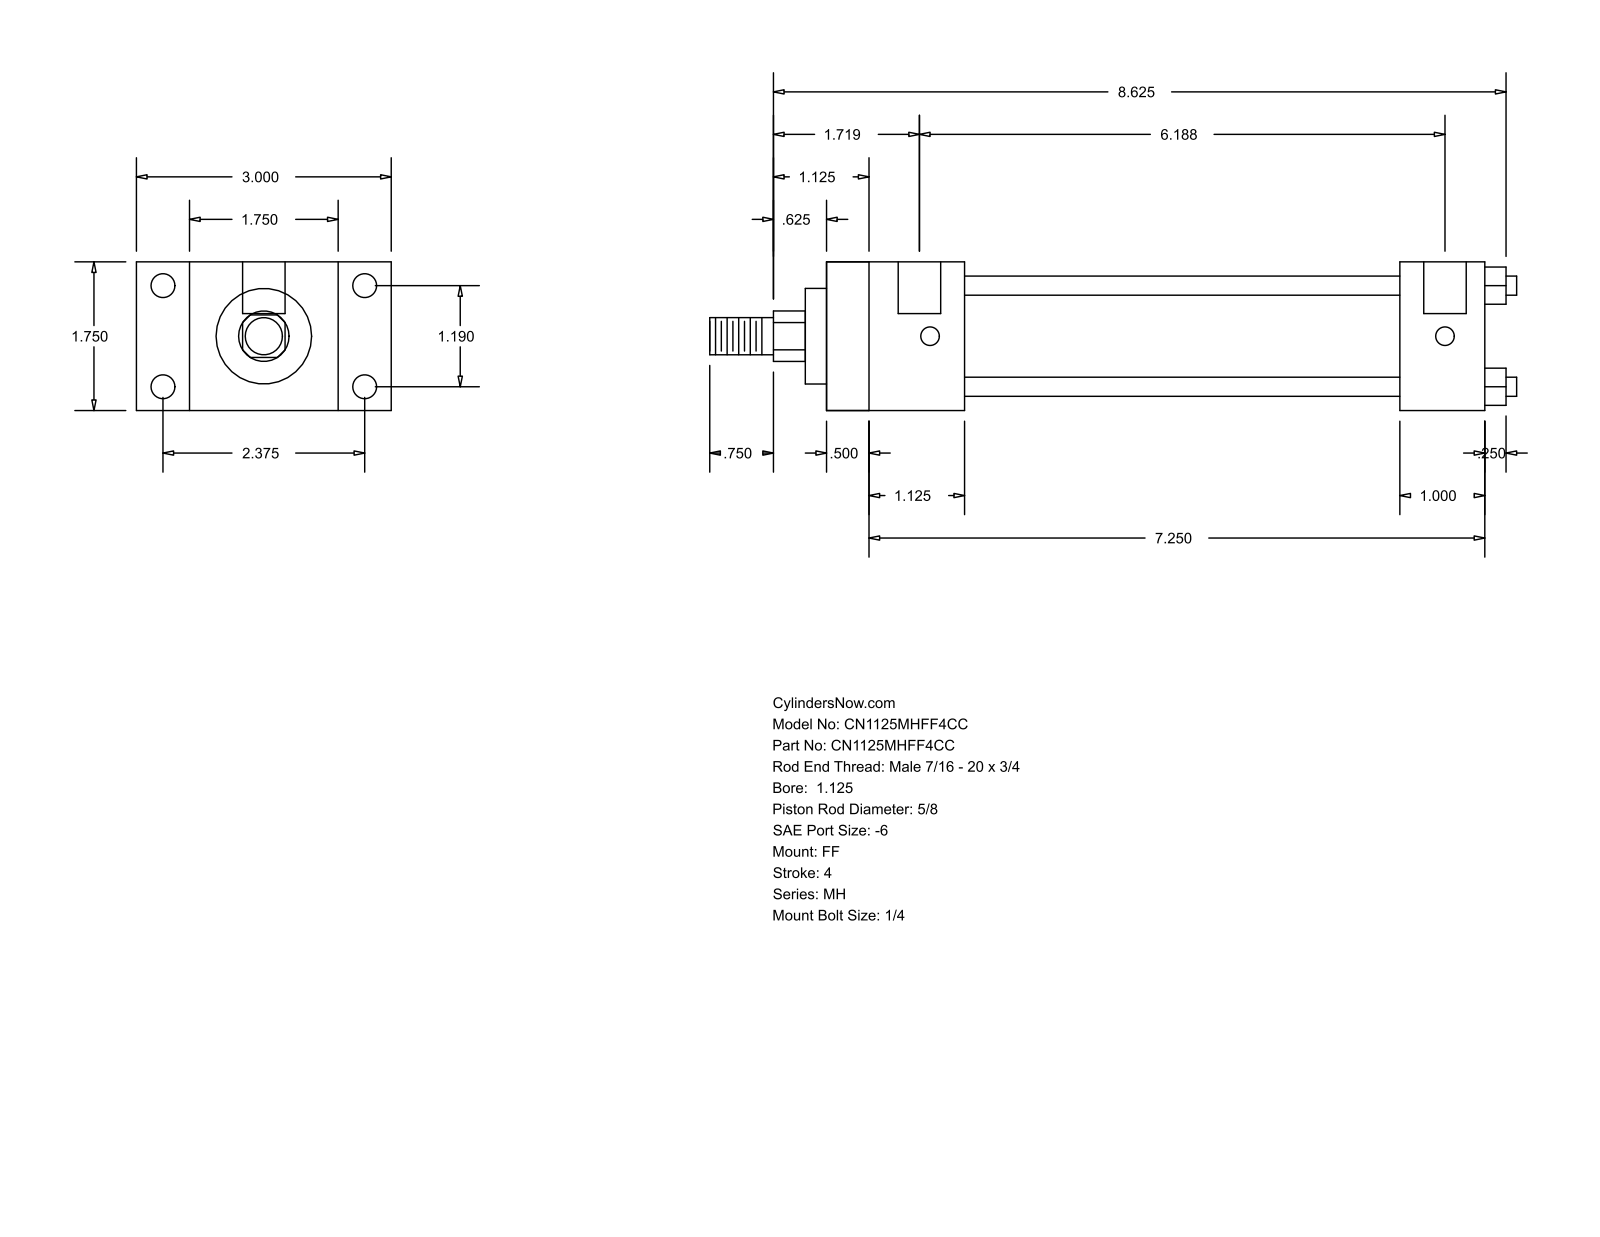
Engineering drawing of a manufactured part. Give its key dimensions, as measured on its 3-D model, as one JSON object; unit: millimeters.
{"part_name": "MH_FF__0112_0.625", "step_written_by": "GSSL Pune (CONFIG_CONTROL_DESIGN)", "units": "millimeters", "bodies": {"solids": 0, "faces": 92, "planar": 64, "cylindrical": 28, "other": 0}, "overall_size": [241.3, 76.2, 44.45], "round_holes": [[5.56, 4], [7.14, 4], [12.7, 2]], "round_bosses_or_shafts": [[5.71, 4], [34.92, 1], [28.57, 1], [15.88, 1], [11.11, 1]], "partial_cylinders_radius": [[7.54, 1]], "face_to_face_distances": [44.46, 196.84, 12.69, 184.15, 15.87, 28.58, 60.33, 25.4, 41.27, 171.44], "hole_center_spacings": [30.22, 60.32, 67.47, 153.99, 3.17, 157.16]}
